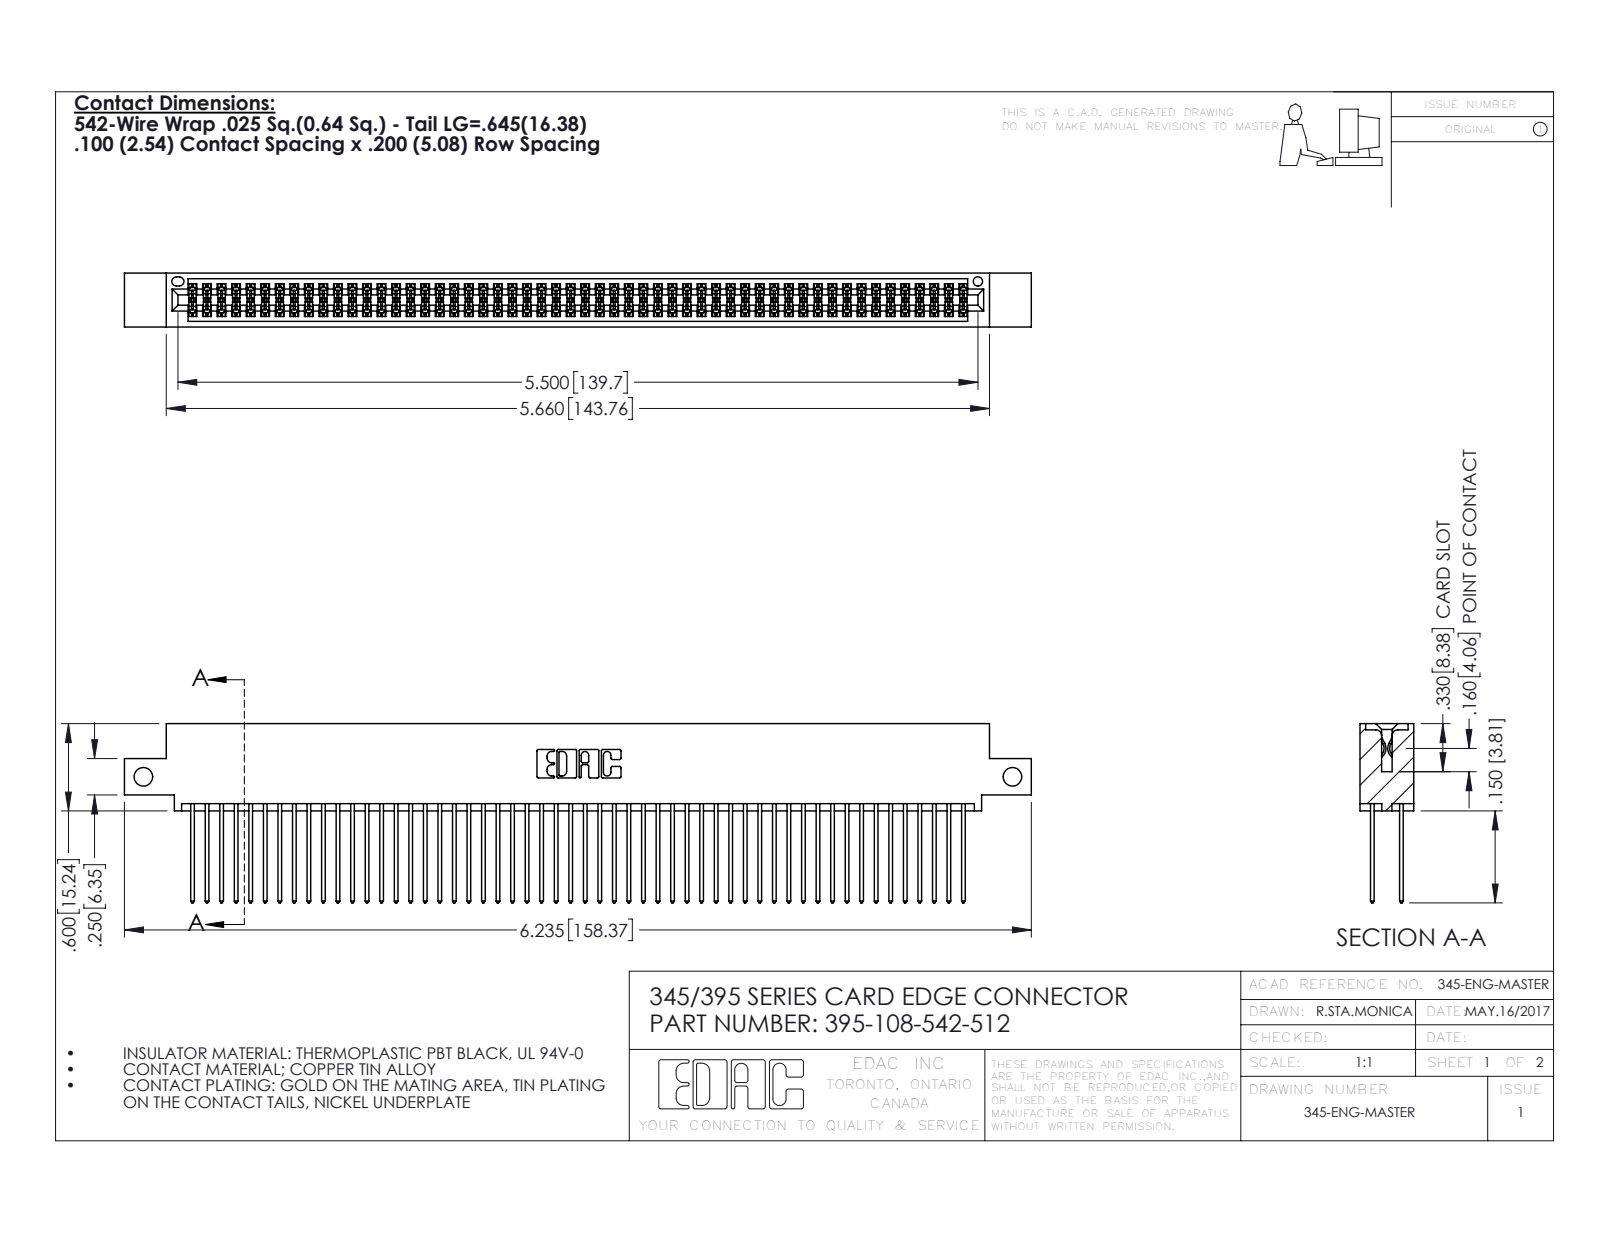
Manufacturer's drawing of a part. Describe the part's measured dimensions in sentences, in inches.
The part is named "395-108-542-512; 345-292-001_345-293-142; 345 Part_0.110 Offset - Side Mount". Its 3-D file was written by "SolidWorks 2016 (CONFIG_CONTROL_DESIGN)". It is 109 solids with 5530 faces: 3648 planar, 1882 cylindrical and 0 other. Overall it measures 6.235 by 1.232 by 0.37 inches. Its volume is 0.967 cubic inches and its surface area 40.23 square inches. Round holes: 2 of diameter 0.128, 1 of diameter 0.064. Partial cylindrical surfaces (rounded edges, fillets, slot ends): 162 of radius 0.006, 108 of radius 0.01, 22 of radius 0.01, 6 of radius 0.007, 6 of radius 0.031, 3 of radius 0.026, 2 of radius 0.014, 2 of radius 0.019. The main face-to-face distances are 0.298, 0.072, 0.2, 0.098, 0.272, 0.025, 0.225, 0.37, 0.175, 0.149. The hole center spacings are 5.975.
